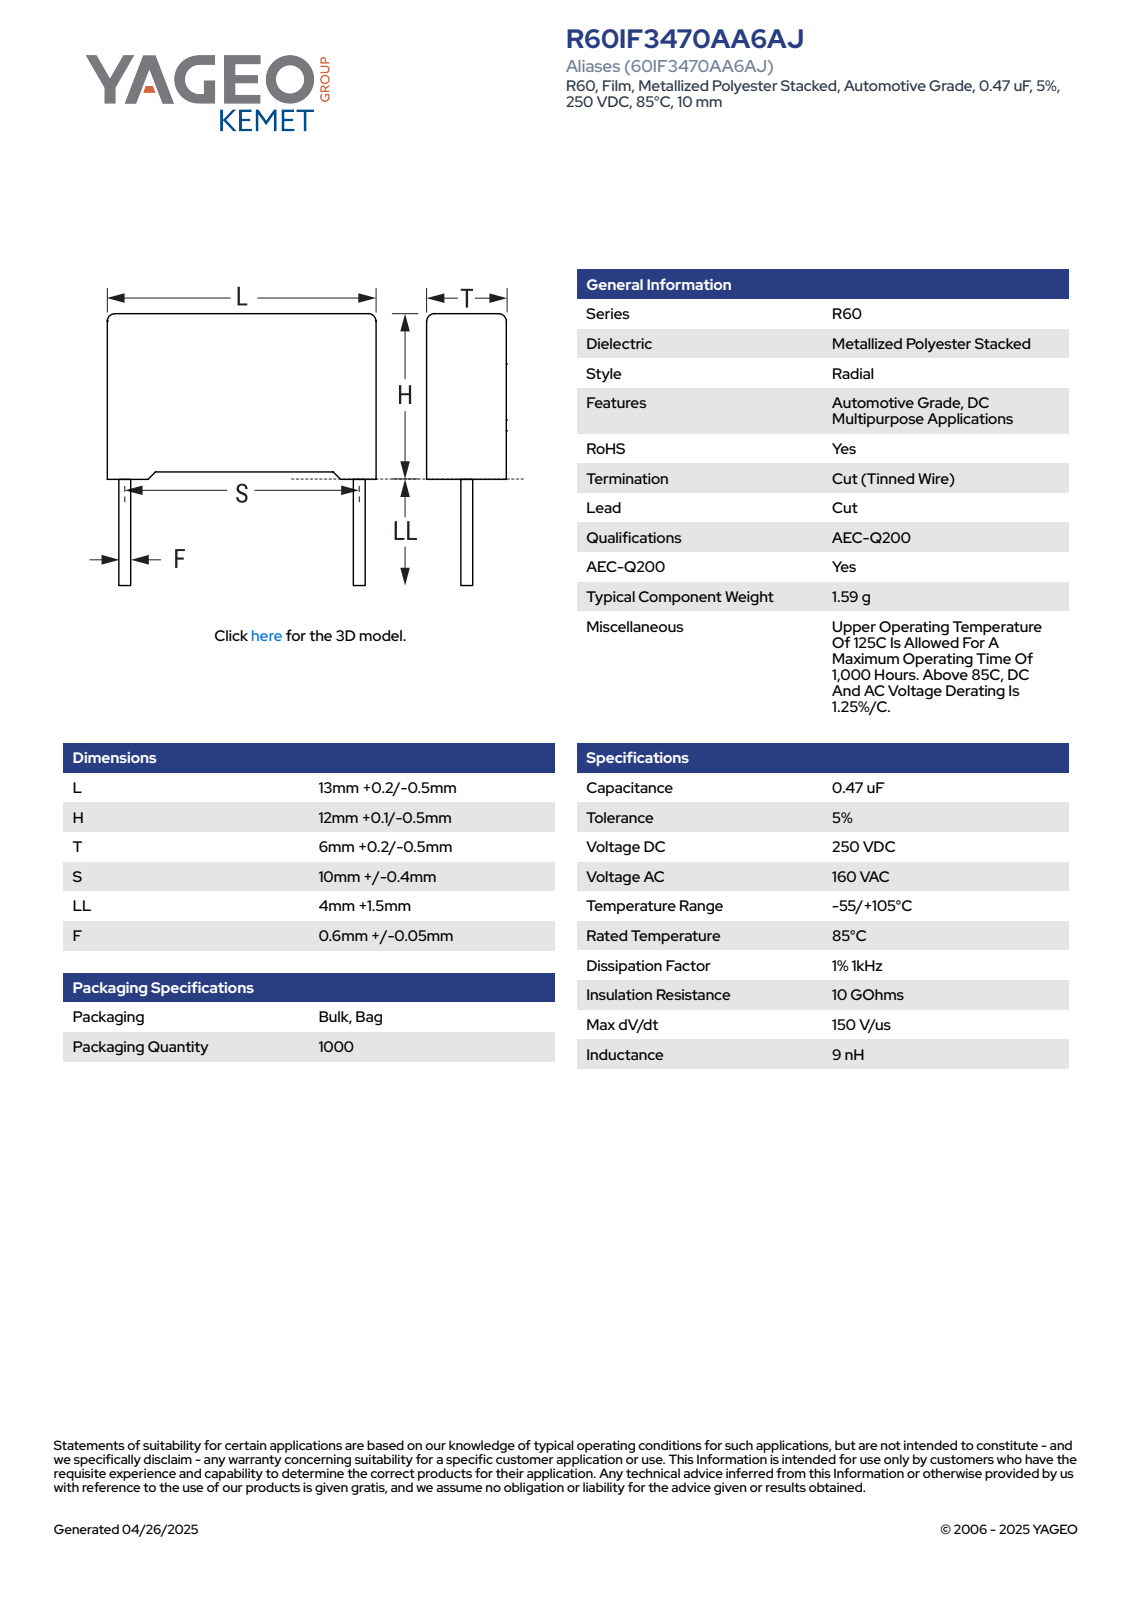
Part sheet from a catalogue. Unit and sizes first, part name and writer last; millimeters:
Units: millimetres
Overall size (bounding box): 17.6 × 13.2 × 6.21
Round bosses / shafts (diameter × count): ⌀0.65 ×2
Partial cylindrical surfaces — rounded edges, fillets, slot ends (radius × count): R0.5 ×4
Main face-to-face distances: 6.2, 13.2, 11.35, 0.44, 5.76, 0.75, 12.1, 12.76, 5.32, 0.42
Volume: 941 mm³ · Surface area: 679 mm²
Bodies: 4 solids, 85 faces (77 planar, 8 cylindrical, 0 other)
Part name (STEP PRODUCT): CFR_RB2_13X12X6_L13.2H12.1T6.2S10LL5.5F0.65
STEP written by: SolidWorks 2021 (AUTOMOTIVE_DESIGN)
